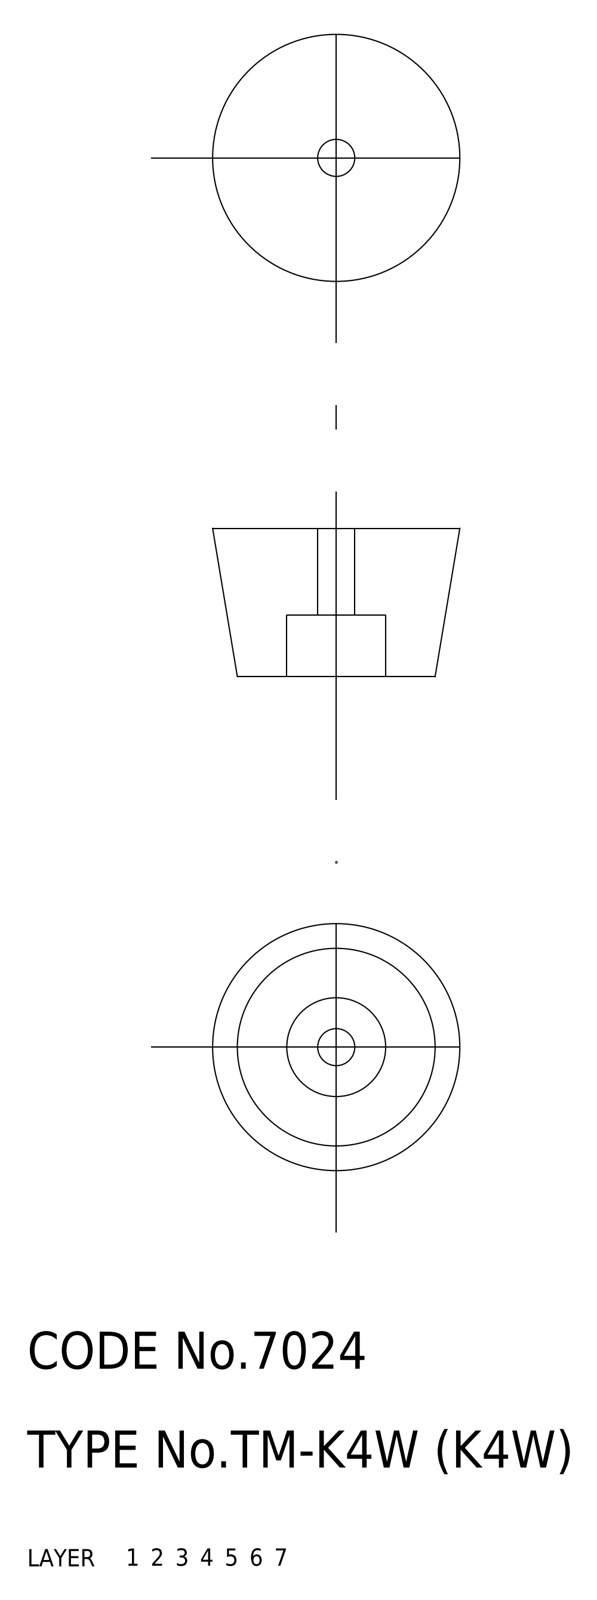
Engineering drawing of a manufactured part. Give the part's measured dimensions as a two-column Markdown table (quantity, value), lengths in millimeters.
| quantity | value |
| --- | --- |
| part name | washer; rubber foot; K4W_6443_36 |
| STEP written by | CADfix (AUTOMOTIVE_DESIGN) |
| units | millimeters |
| bodies | 2 solids, 21 faces (0 planar, 0 cylindrical, 21 other) |
| overall size | 20 × 20 × 12 |
| volume | 2 771 mm³ |
| surface area | 1 631 mm² |
